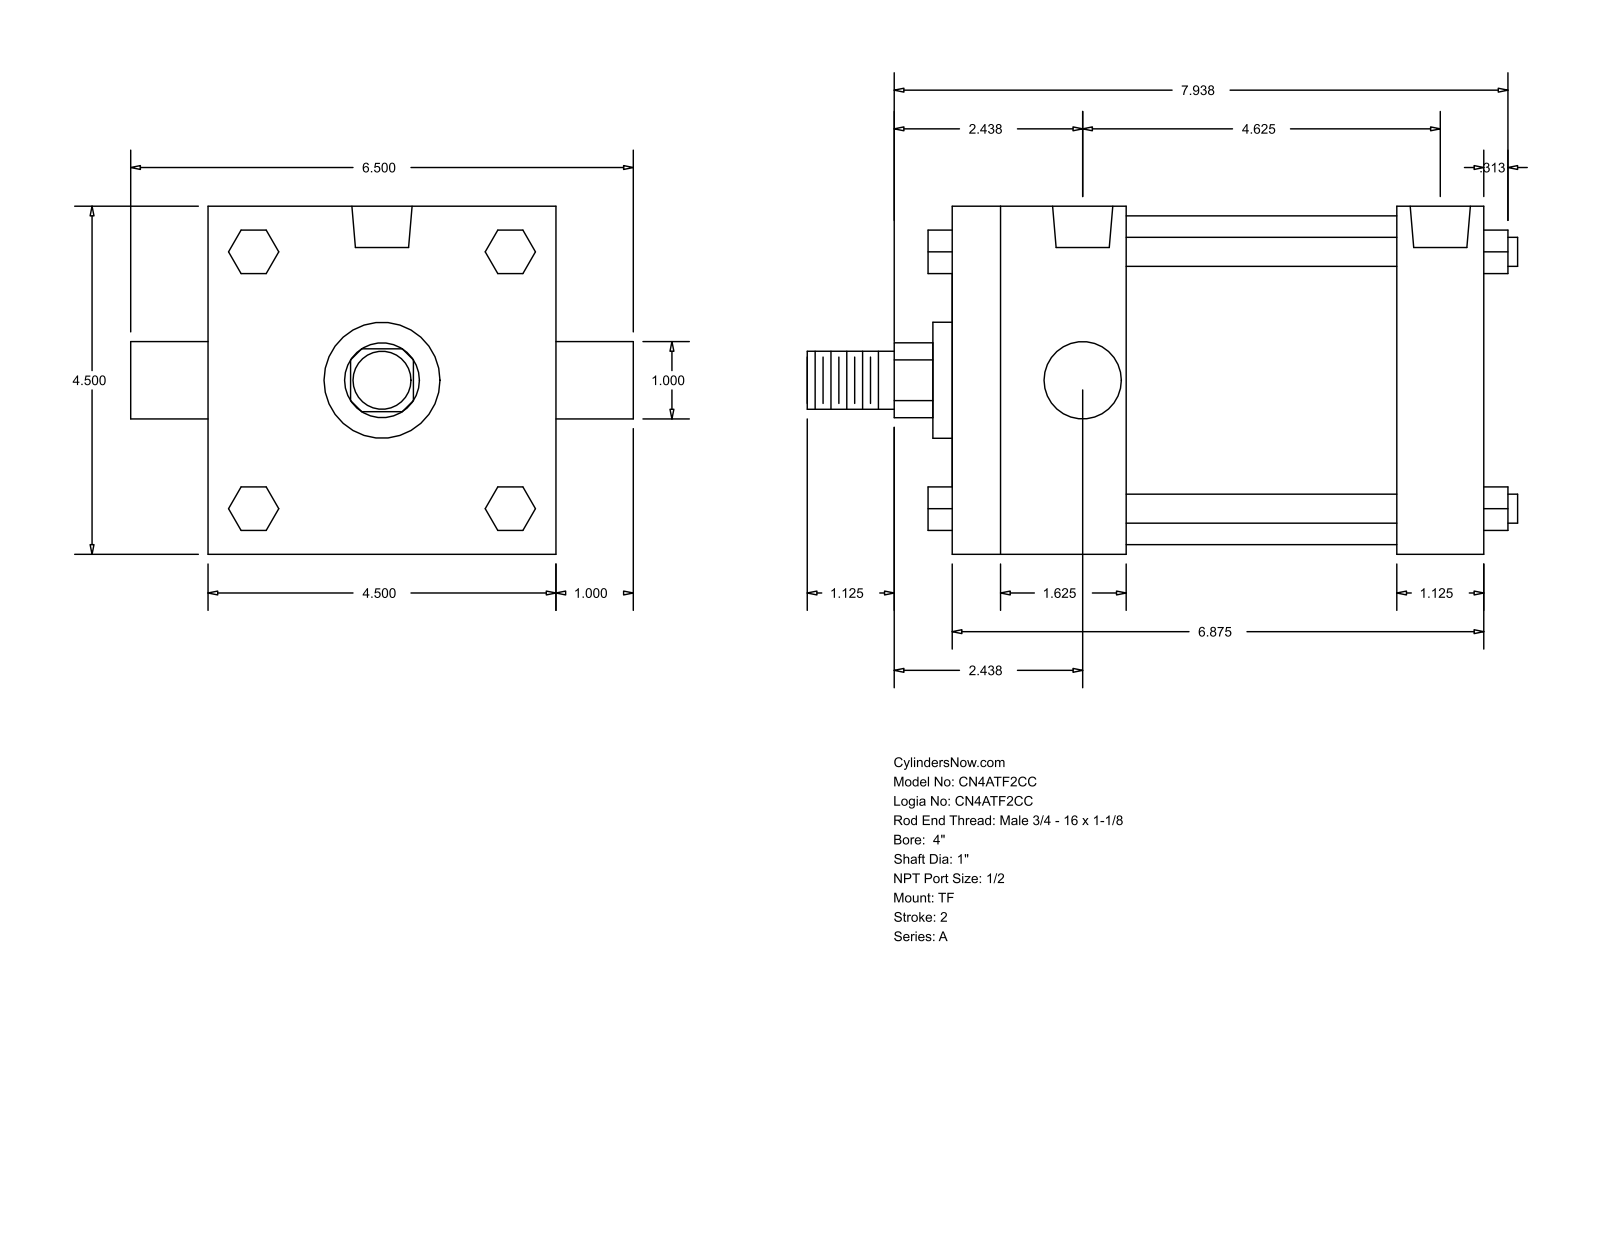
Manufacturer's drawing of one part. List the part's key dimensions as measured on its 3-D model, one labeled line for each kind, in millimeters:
Part name (STEP PRODUCT): A_TF__0400_1
STEP written by: GSSL Pune (CONFIG_CONTROL_DESIGN)
Units: millimetres
Bodies: 0 solids, 120 faces (92 planar, 28 cylindrical, 0 other)
Overall size (bounding box): 233.36 × 165.1 × 114.3
Round holes (diameter × count): ⌀8.73 ×3, ⌀19.77 ×2
Round bosses / shafts (diameter × count): ⌀9.53 ×4, ⌀25.4 ×2, ⌀107.95 ×1, ⌀38.1 ×1, ⌀19.05 ×1
Partial cylindrical surfaces — rounded edges, fillets, slot ends (radius × count): R12.29 ×1
Main face-to-face distances: 114.3, 174.63, 146.05, 28.58, 57.15, 88.9, 117.48, 14.29, 42.16, 73.03
Hole centre spacings: 3.18, 114.3, 111.12, 117.48
